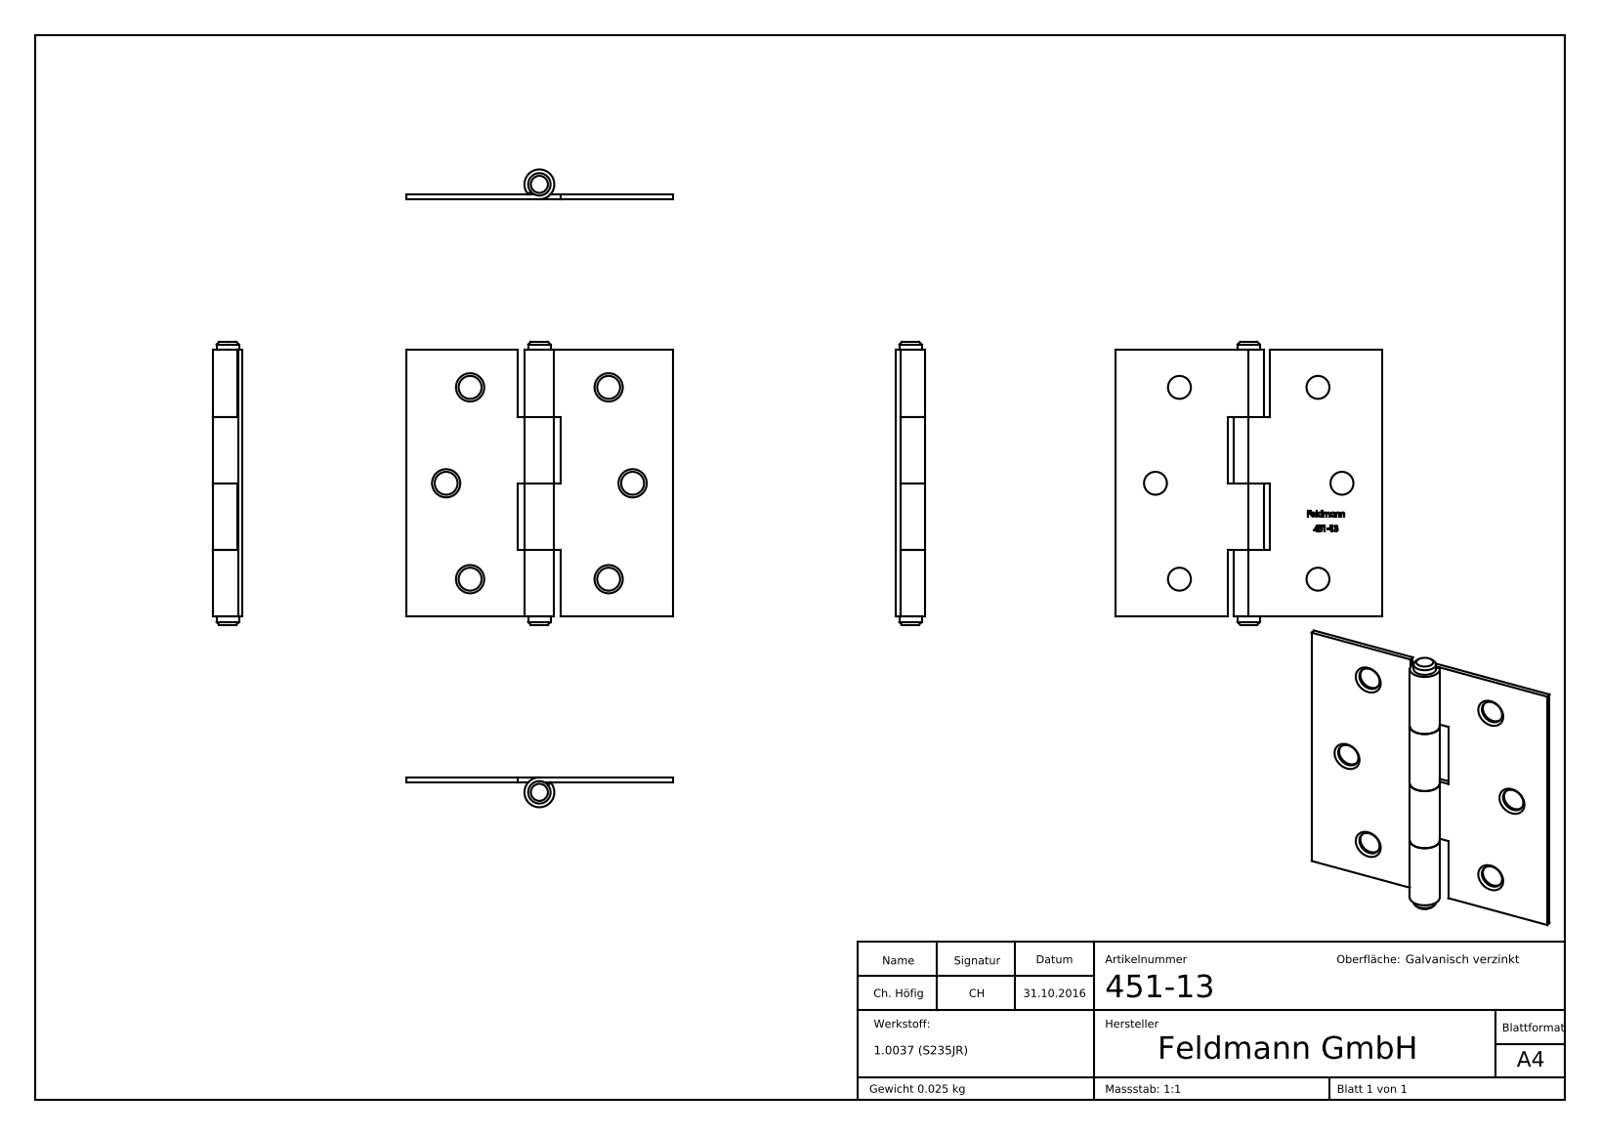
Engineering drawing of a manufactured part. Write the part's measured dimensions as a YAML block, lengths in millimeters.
part_name: "451-13 Teil1; 451-13 Teil2; 451-13; 451-13 Teil3"
step_written_by: "SolidWorks 2018 (CONFIG_CONTROL_DESIGN)"
units: millimeters
bodies: {solids: 3, faces: 233, planar: 138, cylindrical: 17, other: 78}
overall_size: [53.1, 50, 5.6]
volume: 3160
surface_area: 6787
round_holes:
  - {diameter: 4.3, count: 6}
  - {diameter: 3.8, count: 1}
round_bosses_or_shafts:
  - {diameter: 5.6, count: 1}
  - {diameter: 4.2, count: 1}
face_to_face_distances: [0.9, 12.5, 50, 25, 37.5, 21, 29, 8, 1.55, 14.05]
hole_center_spacings: [18.55, 35.42, 26, 36, 44.41, 35]
